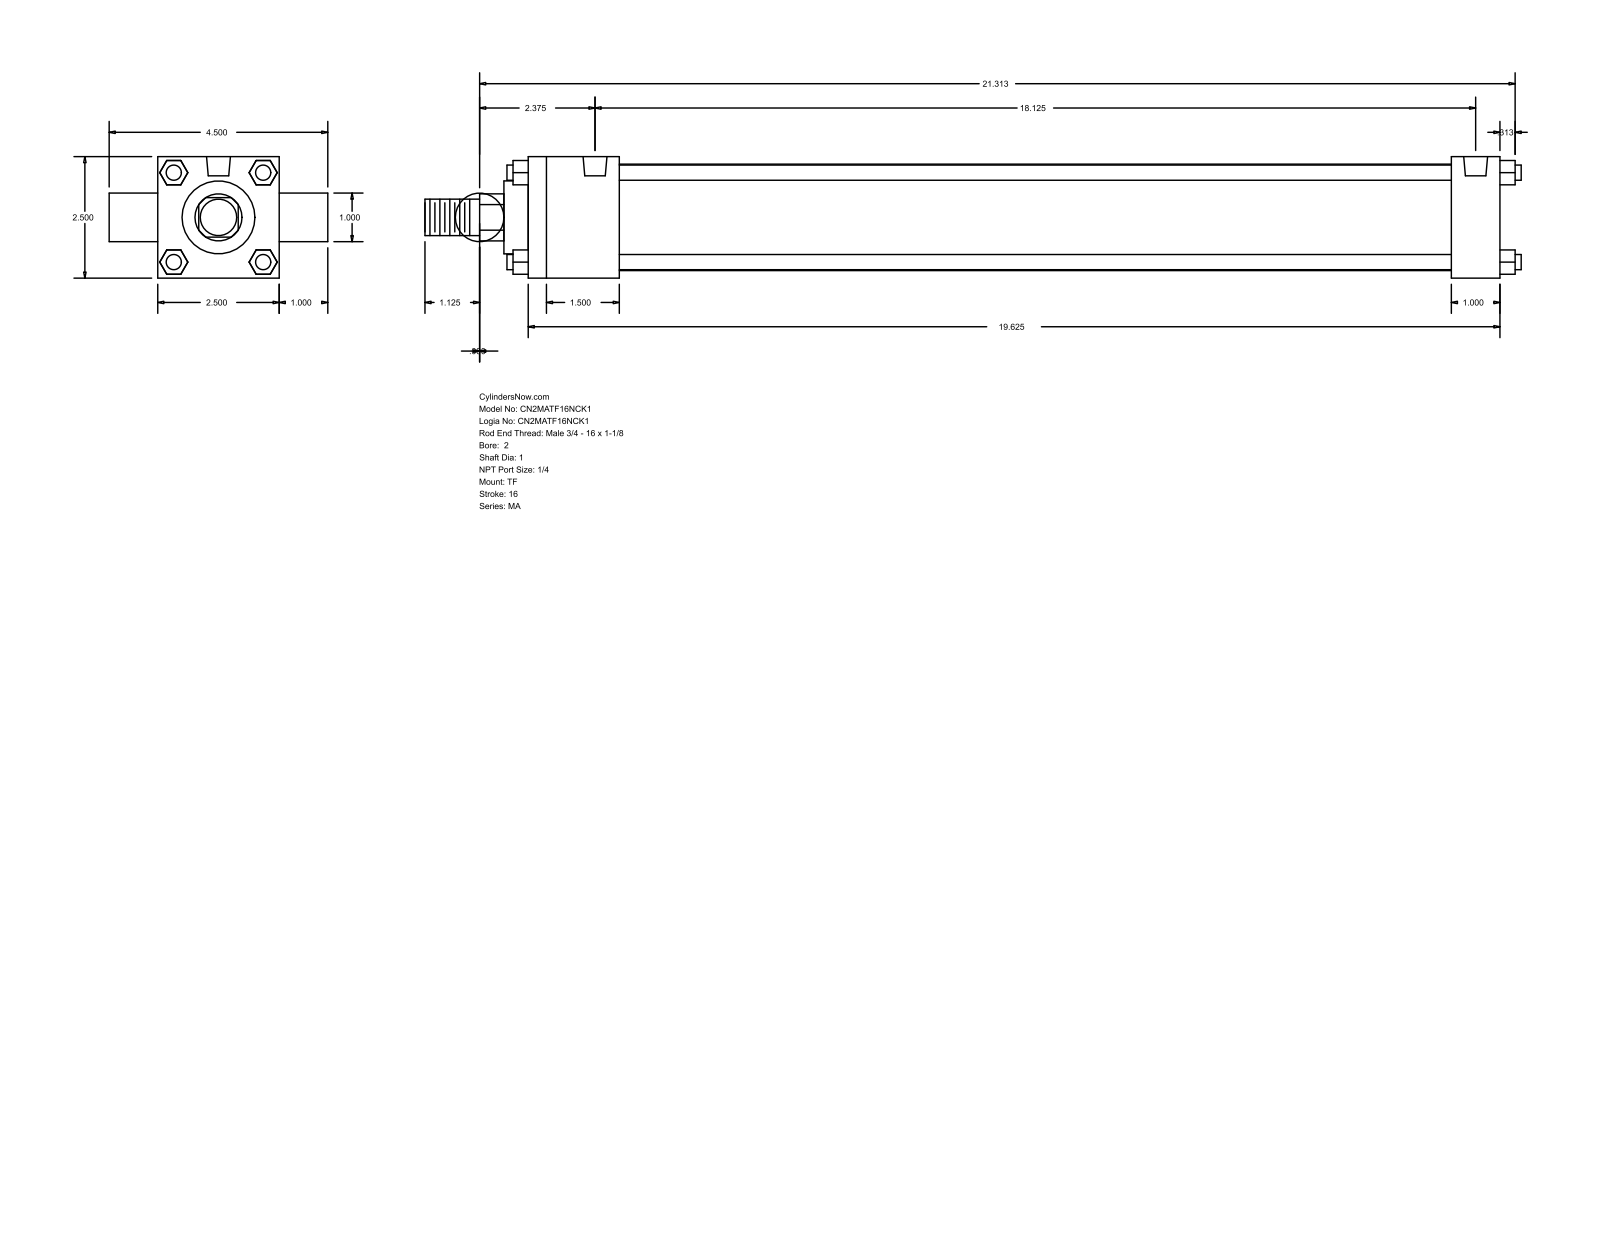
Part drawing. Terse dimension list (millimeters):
name: MA_TF__0200_1
written by: GSSL Pune (CONFIG_CONTROL_DESIGN)
unit: mm
bodies: 0 solids, 120 faces (92 planar, 28 cylindrical, 0 other)
size: 573.09 × 114.3 × 63.5
holes: 3× ⌀7.94, 2× ⌀12.49
bosses: 4× ⌀7.94, 2× ⌀25.4, 1× ⌀55.63, 1× ⌀38.1, 1× ⌀19.05
rounds: 1× R12.29
face distances: 63.5, 25.4, 508, 12.7, 47.63, 482.6, 434.97, 460.37, 88.9, 23.37
hole spacings: 460.37
